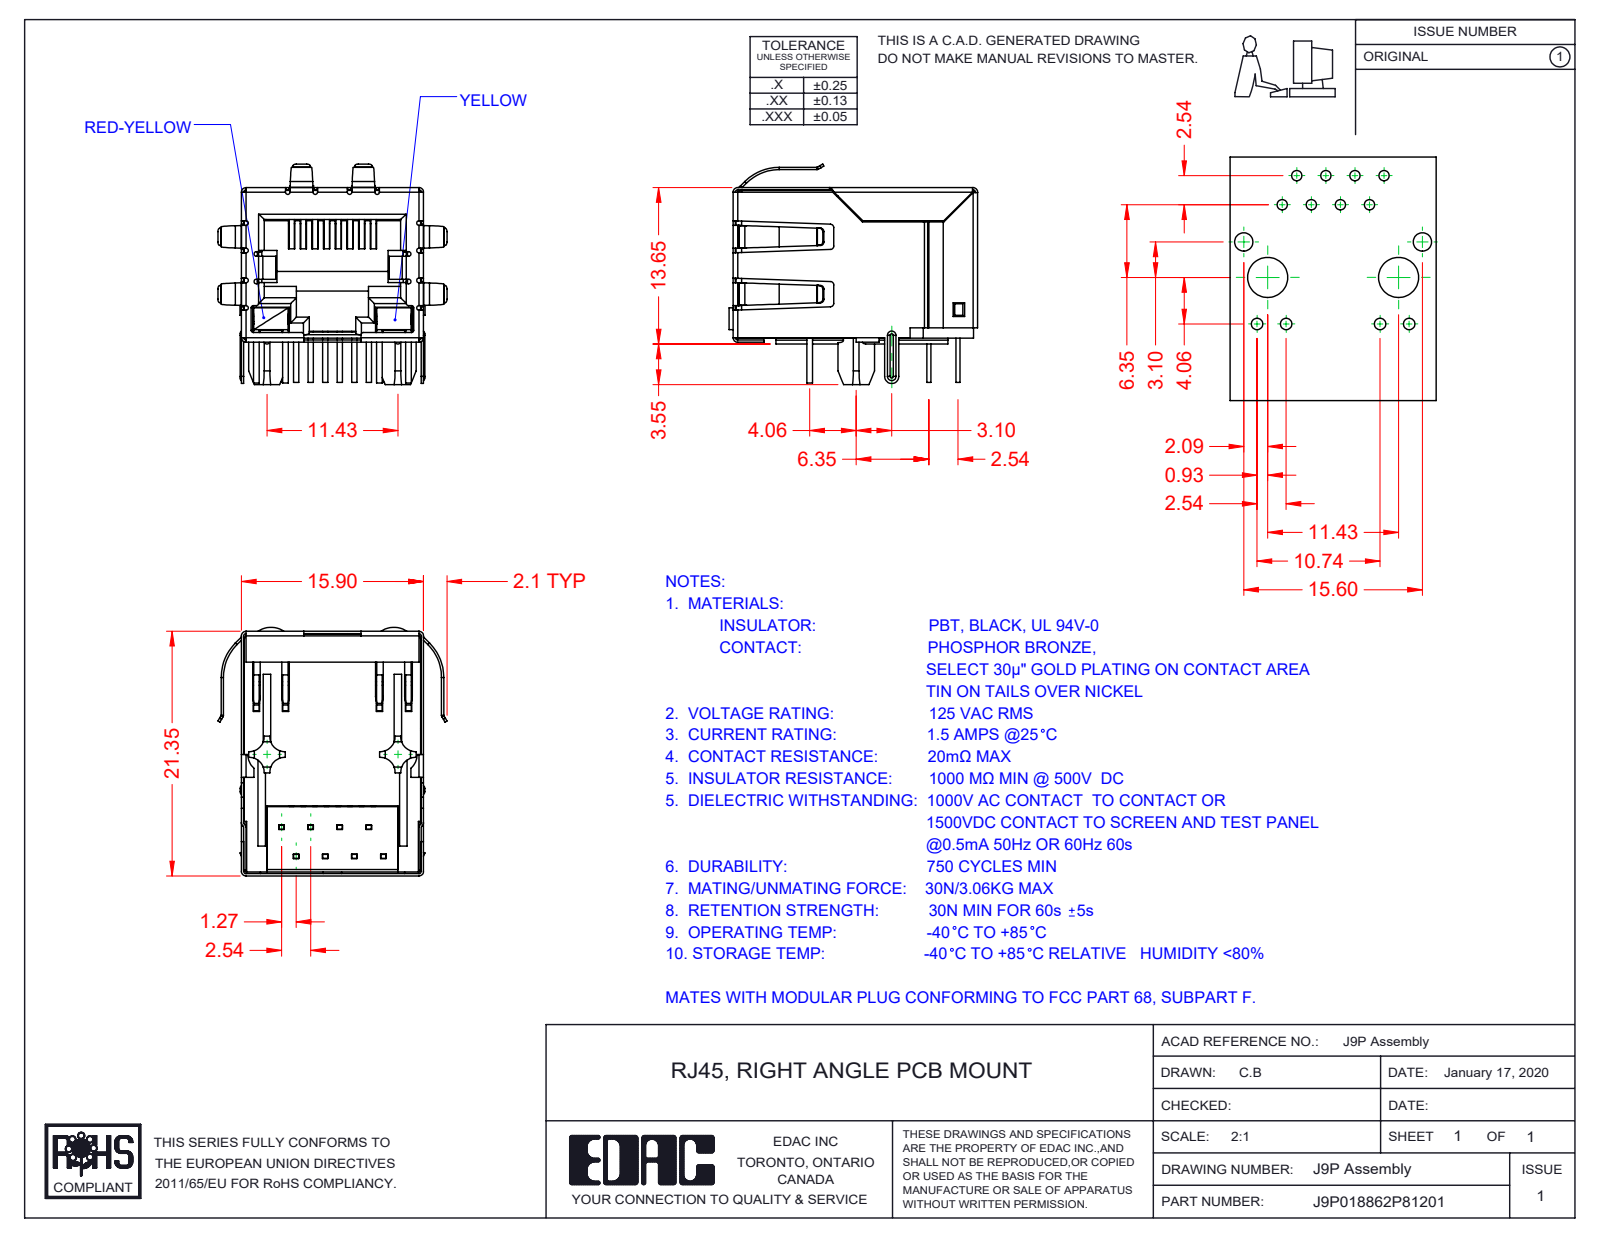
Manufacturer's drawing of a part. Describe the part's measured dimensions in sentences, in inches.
The part is named "9P-LED Assembly; 9P-LED Contact Lock; 9P-LED Contacts; 9P-LED Insulator (+4 more)". Its 3-D file was written by "SolidWorks 2016 (CONFIG_CONTROL_DESIGN)". It is 13 solids with 1474 faces: 1042 planar, 338 cylindrical and 94 other. Overall it measures 0.854 by 0.787 by 0.758 inches. Its volume is 0.164 cubic inches and its surface area 11.65 square inches. Partial cylindrical surfaces (rounded edges, fillets, slot ends): 39 of radius 0.008, 22 of radius 0.02, 20 of radius 0.012, 16 of radius 0.016, 8 of radius 0.051, 5 of radius 0.009, 4 of radius 0.004, 4 of radius 0.012. The main face-to-face distances are 0.608, 0.618, 0.616, 0.014, 0.021, 0.61, 0.487, 0.024, 0.055, 0.023.
